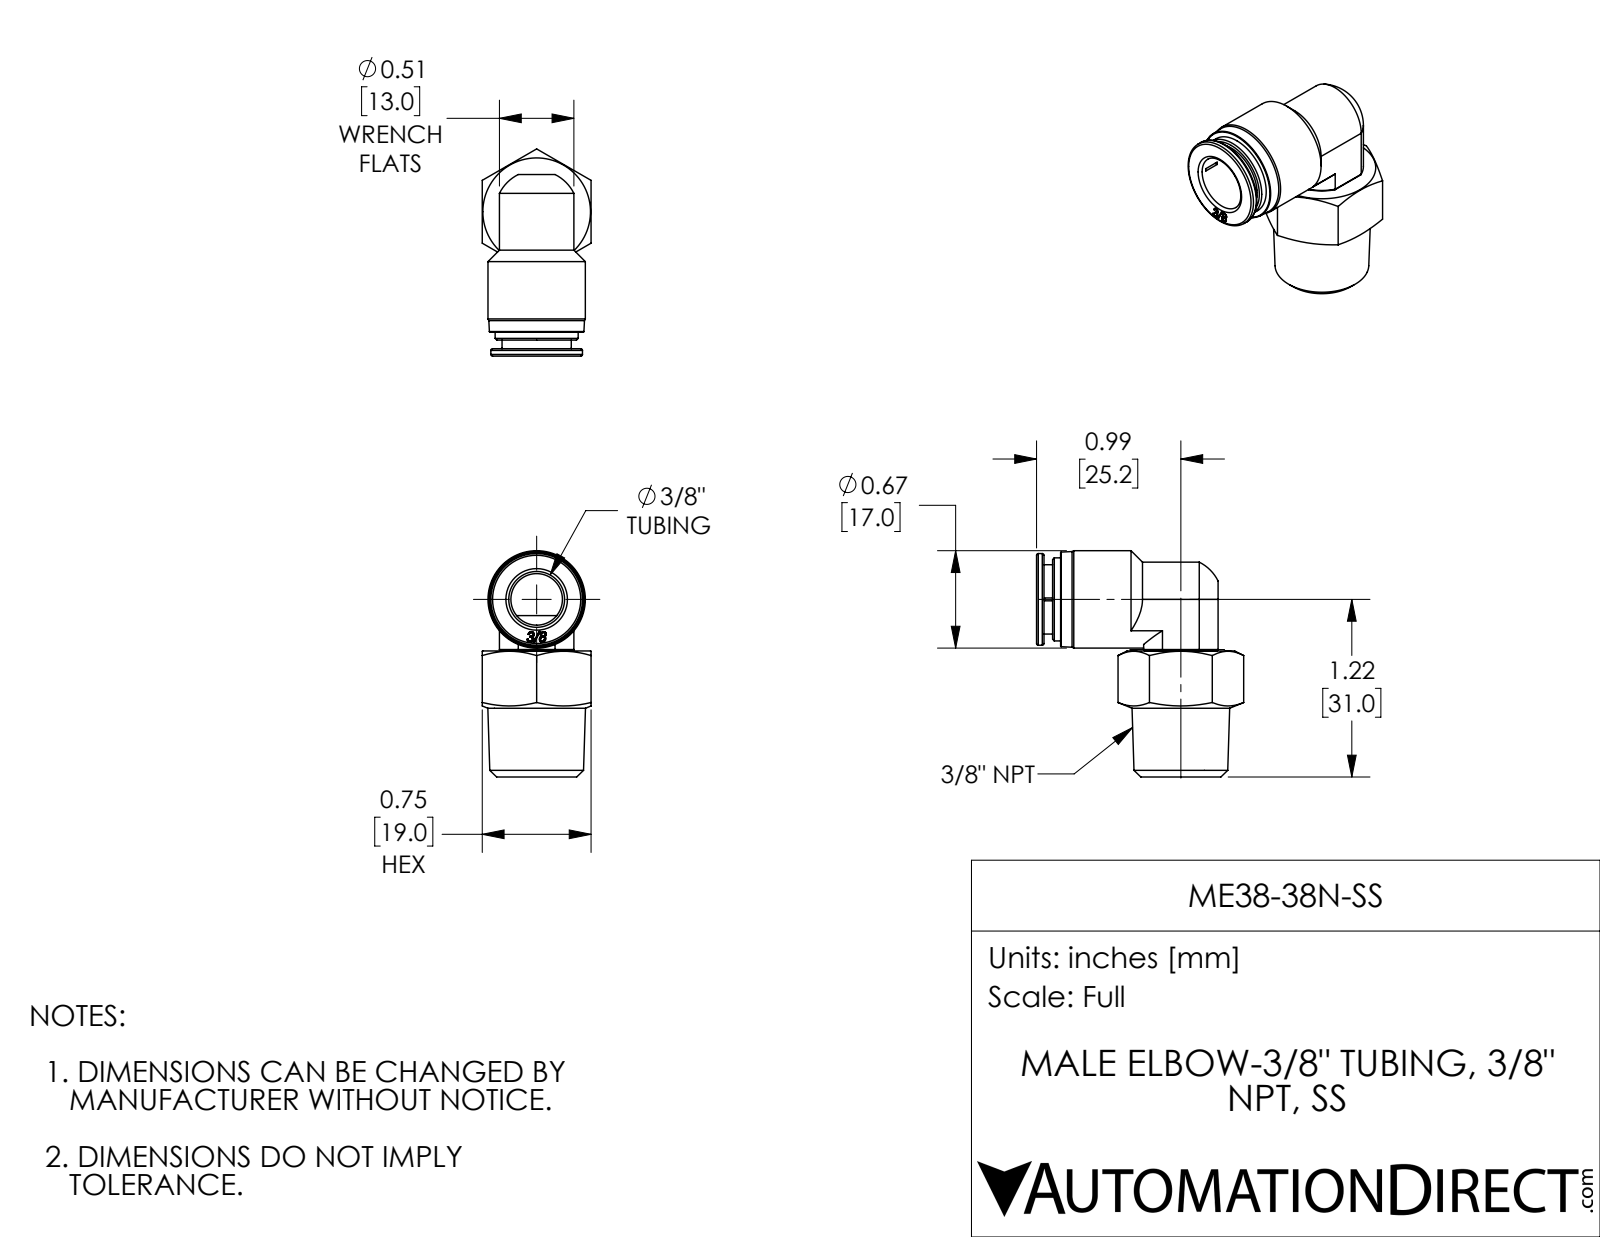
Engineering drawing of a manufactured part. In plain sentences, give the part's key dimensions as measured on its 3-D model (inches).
The part is named "ME38-38N-SS". Its 3-D file was written by "SolidWorks 2017 (AUTOMOTIVE_DESIGN)". It is 2 solids with 140 faces: 39 planar, 29 cylindrical and 72 other. Overall it measures 1.555 by 1.424 by 0.748 inches. Its volume is 0.527 cubic inches and its surface area 8.982 square inches. Round holes: 1 of diameter 0.276, 1 of diameter 0.354, 1 of diameter 0.356, 1 of diameter 0.384. Round bosses or shafts: 1 of diameter 0.669, 1 of diameter 0.63, 1 of diameter 0.571, 1 of diameter 0.476, 1 of diameter 0.354. Partial cylindrical surfaces (rounded edges, fillets, slot ends): 4 of radius 0.008, 1 of radius 0.256, 1 of radius 0.285. The main face-to-face distances are 0.748, 0.118, 0.63, 0.866, 0.512, 0.868, 1.248, 0.051, 1.197, 0.165.
